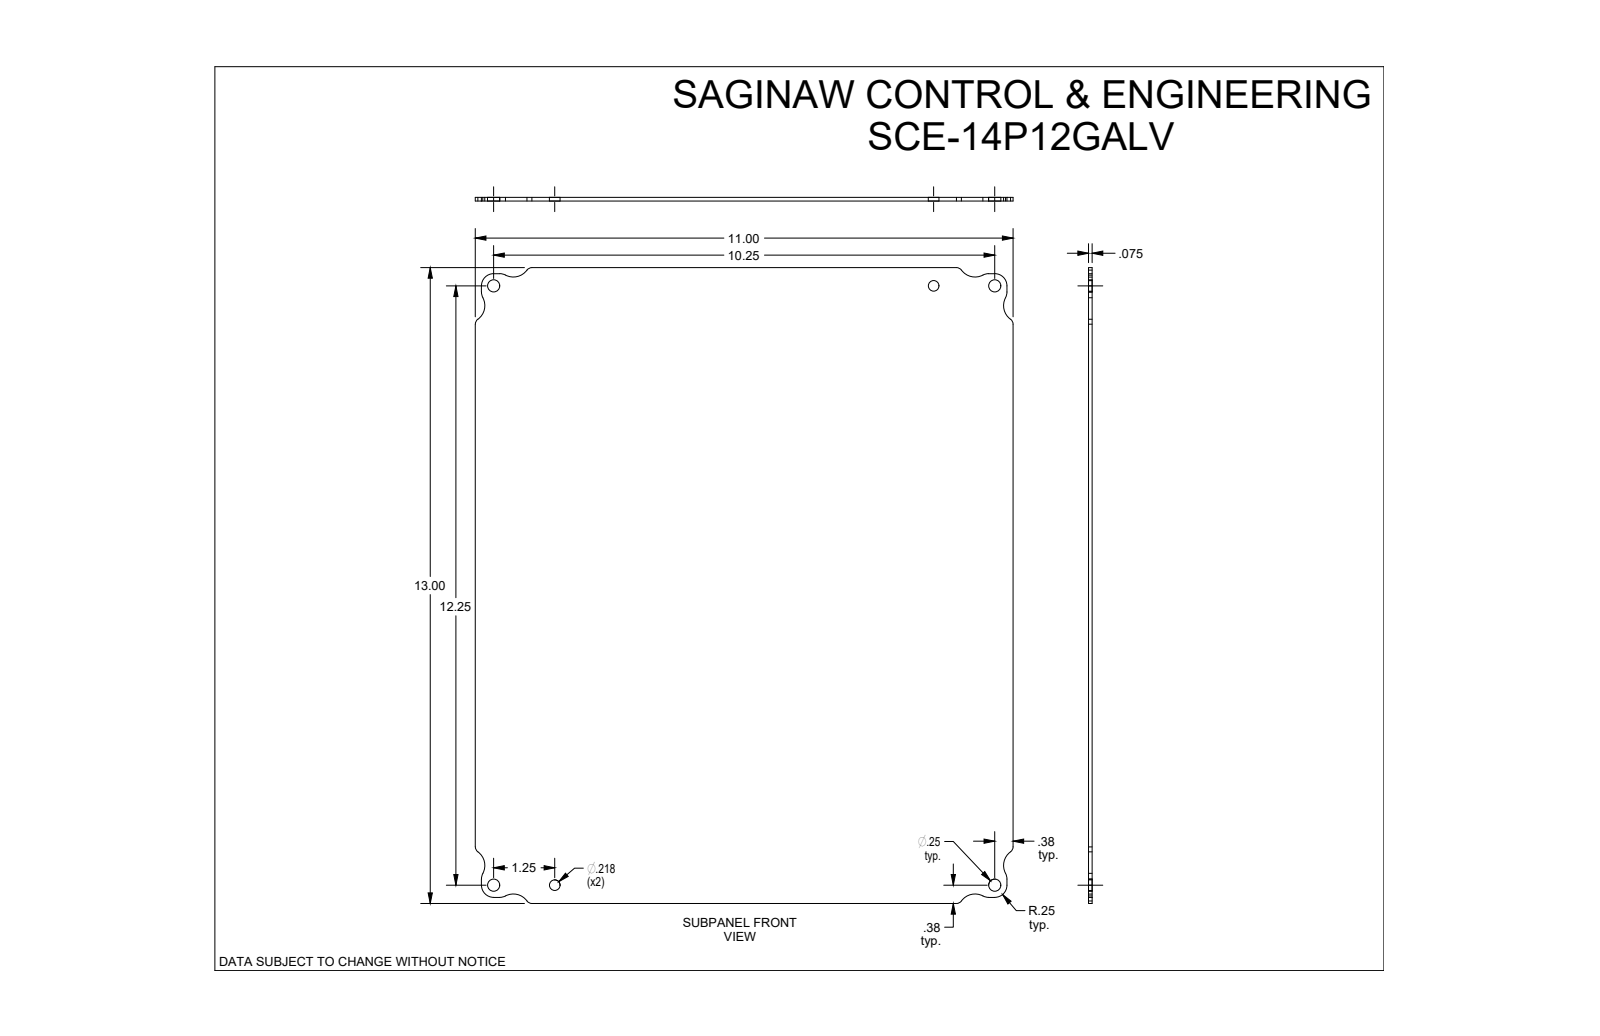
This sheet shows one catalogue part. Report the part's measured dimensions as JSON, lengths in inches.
{"part_name": "SCE-14P12GALV", "step_written_by": "SolidWorks 2019 (CONFIG_CONTROL_DESIGN)", "units": "inches", "bodies": {"solids": 1, "faces": 48, "planar": 14, "cylindrical": 34, "other": 0}, "overall_size": [13, 11, 0.075], "volume_in3": 10.61, "surface_area_in2": 286.9, "round_holes": [[0.25, 4], [0.218, 2]], "partial_cylinders_radius": [[0.25, 12], [0.125, 8], [0.344, 8]], "face_to_face_distances": [0.075, 11, 13, 0.125, 10.875, 0.125, 12.875, 10.75, 12.75], "hole_center_spacings": [1.25, 9, 10.25, 12.25, 12.313, 15.2, 15.972, 14.495]}
